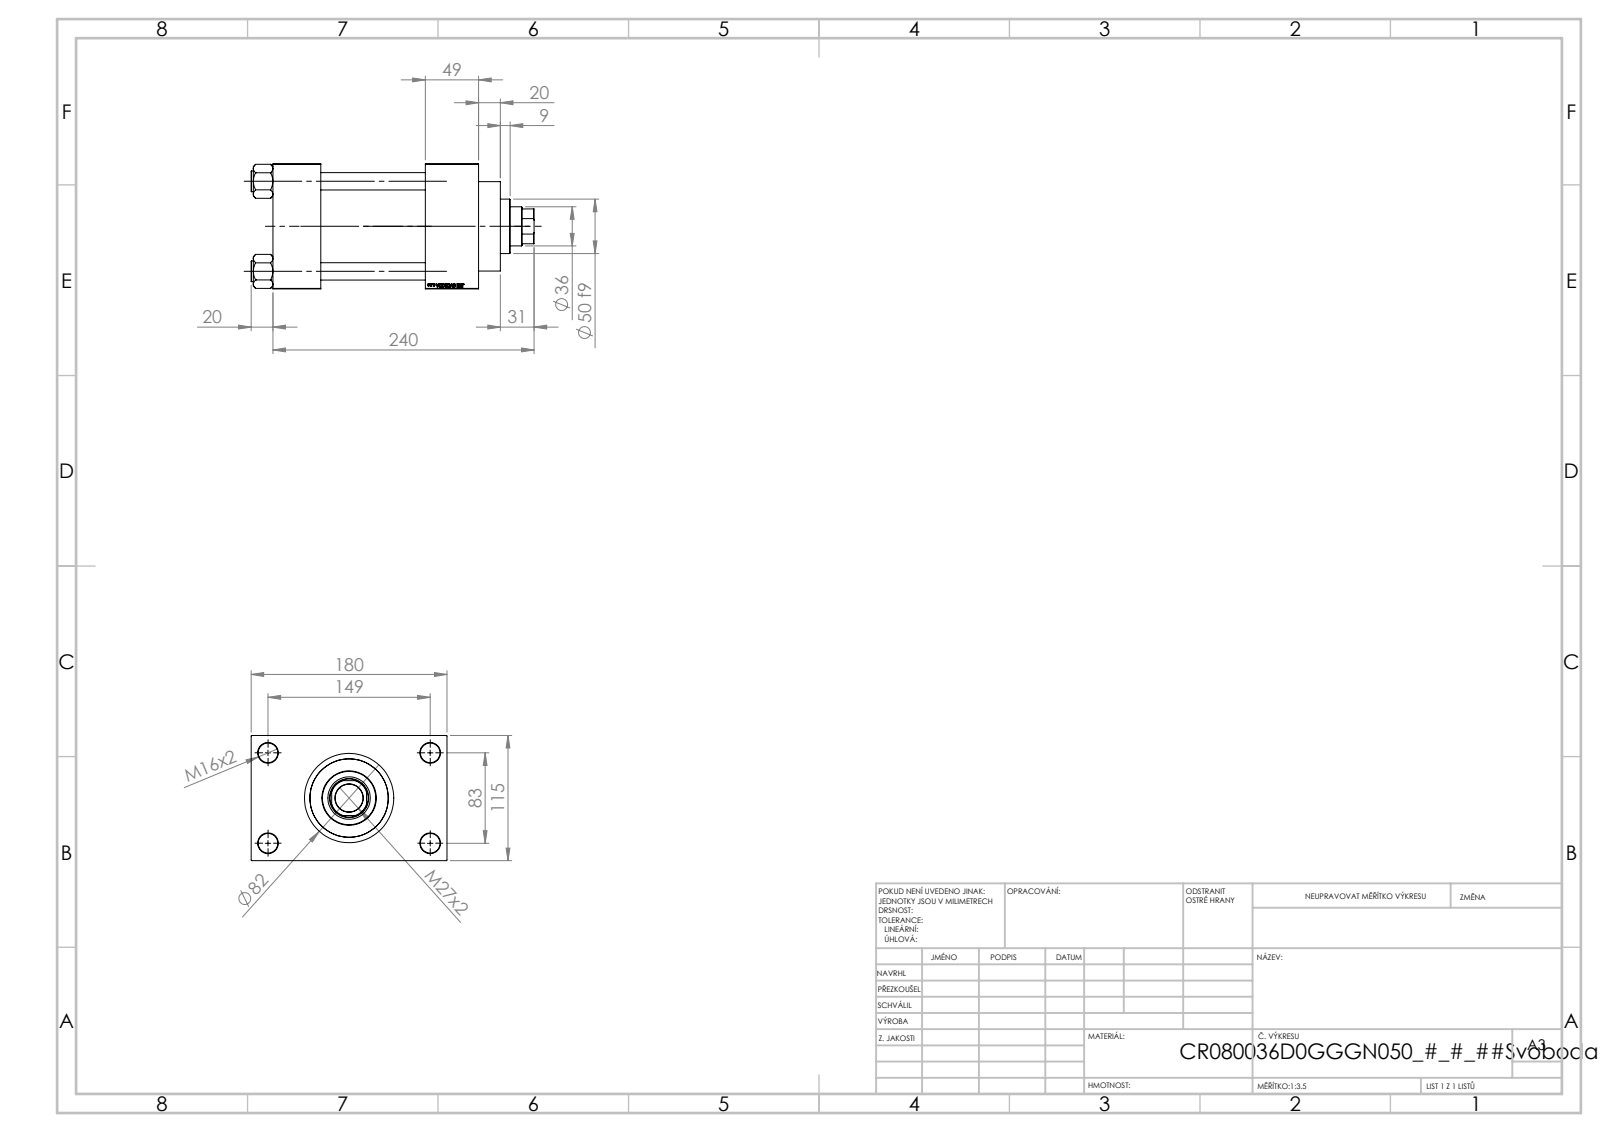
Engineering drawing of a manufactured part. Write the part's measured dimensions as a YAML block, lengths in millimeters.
part_name: "V215CR_VCP_D; V215CR_D_TYCINKA; V215CR_D_Body; V215_VC_A (+1 more)"
step_written_by: "SolidWorks 2019 (CONFIG_CONTROL_DESIGN)"
units: millimeters
bodies: {solids: 11, faces: 1152, planar: 545, cylindrical: 89, other: 518}
overall_size: [260, 180, 115]
volume: 2075000
surface_area: 318973
round_holes:
  - {diameter: 16, count: 4}
  - {diameter: 18, count: 4}
  - {diameter: 7, count: 2}
  - {diameter: 26.44, count: 2}
  - {diameter: 35, count: 2}
  - {diameter: 25.5, count: 1}
  - {diameter: 36, count: 1}
  - {diameter: 39, count: 1}
  - {diameter: 61, count: 1}
  - {diameter: 72, count: 1}
  - {diameter: 80, count: 1}
round_bosses_or_shafts:
  - {diameter: 19, count: 4}
  - {diameter: 86, count: 1}
  - {diameter: 82, count: 1}
  - {diameter: 50, count: 1}
partial_cylinders:
  - {radius: 17.5, count: 1}
face_to_face_distances: [115, 96, 145, 49, 44, 140, 189, 32.5, 147.5, 180]
hole_center_spacings: [33.15, 58.48, 82.7, 85.28, 89.24, 115.85, 142.43, 83]
